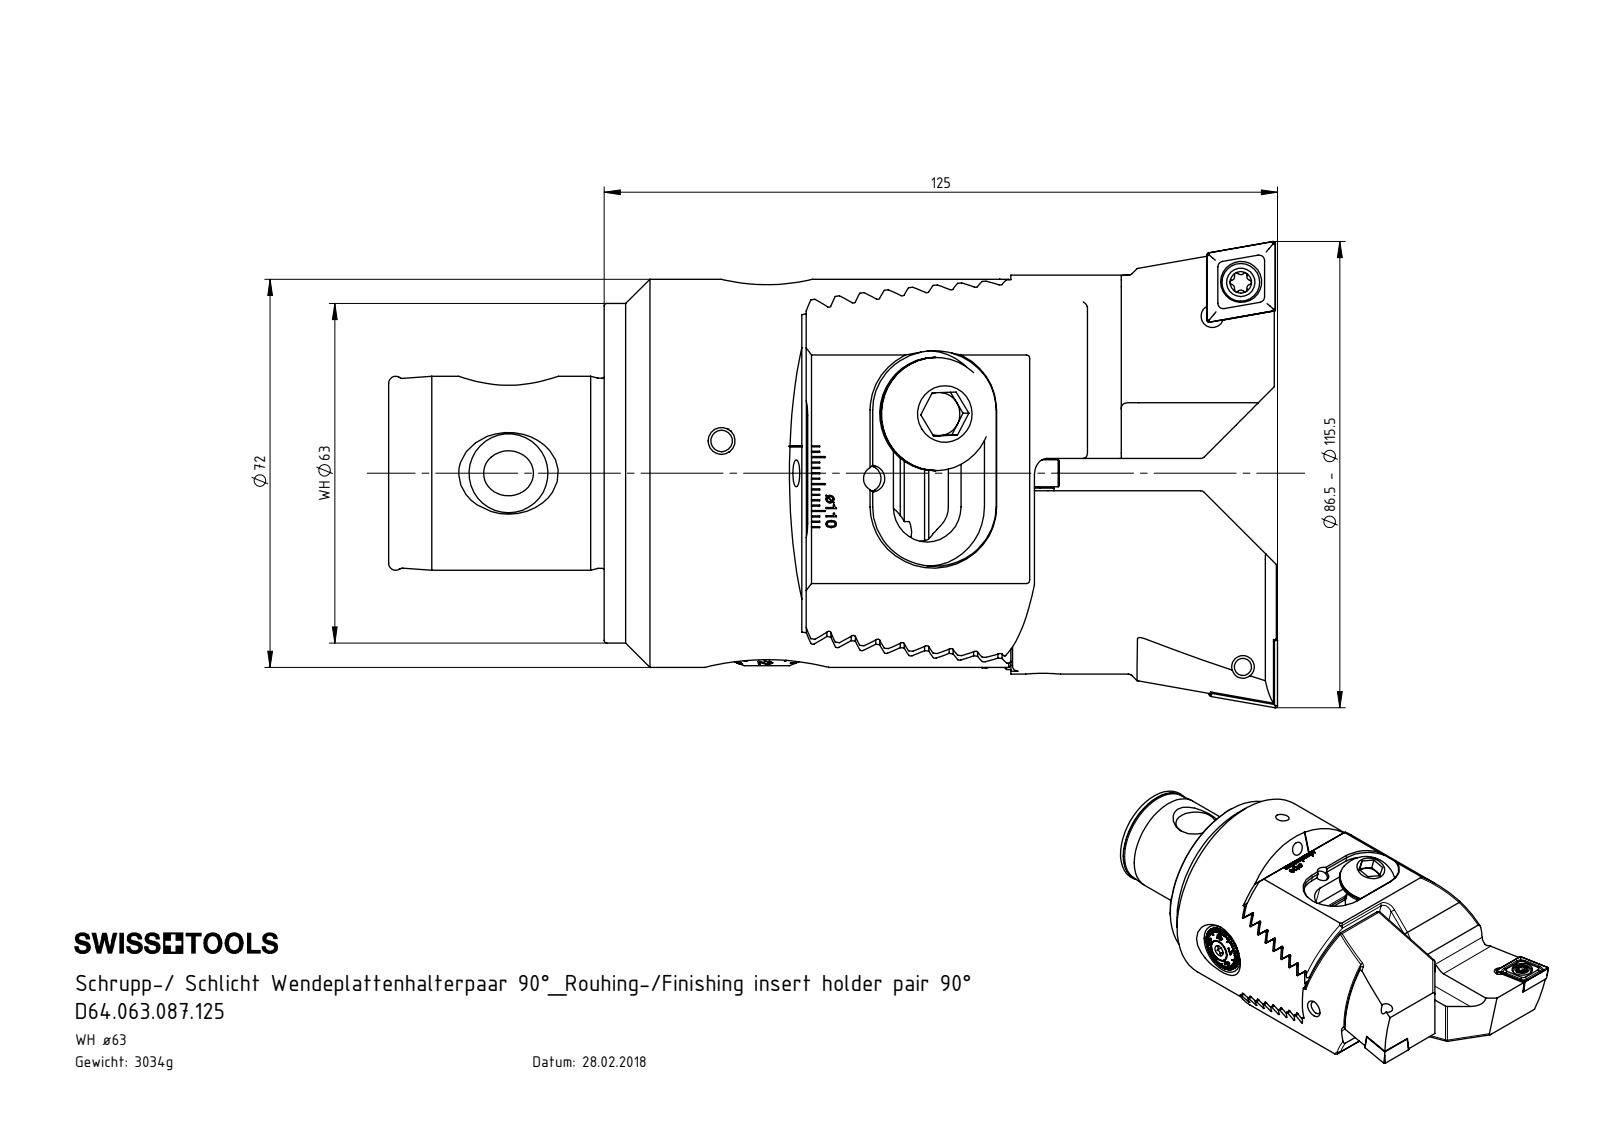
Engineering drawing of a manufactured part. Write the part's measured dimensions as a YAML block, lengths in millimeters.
part_name: "ZC7-WCC.010.050; ZC7-xxx.001.050_A_versetzt Combi; F32-BG2.017.003_A; D64.063.087.125 (+8 more)"
step_written_by: "SolidWorks 2017 (CONFIG_CONTROL_DESIGN)"
units: millimeters
bodies: {solids: 22, faces: 1551, planar: 797, cylindrical: 289, other: 465}
overall_size: [165, 86.5, 72]
volume: 387635
surface_area: 89754
round_holes:
  - {diameter: 5, count: 7}
  - {diameter: 4.2, count: 4}
  - {diameter: 2, count: 2}
  - {diameter: 3, count: 2}
  - {diameter: 5.5, count: 2}
  - {diameter: 7.6, count: 2}
  - {diameter: 10.25, count: 2}
  - {diameter: 13, count: 2}
  - {diameter: 13.5, count: 2}
  - {diameter: 2.5, count: 1}
  - {diameter: 2.9, count: 1}
  - {diameter: 3.3, count: 1}
round_bosses_or_shafts:
  - {diameter: 21, count: 4}
  - {diameter: 5, count: 4}
  - {diameter: 12, count: 2}
  - {diameter: 7, count: 2}
  - {diameter: 4, count: 2}
  - {diameter: 72, count: 1}
  - {diameter: 63, count: 1}
  - {diameter: 36, count: 1}
partial_cylinders:
  - {radius: 0.34, count: 18}
  - {radius: 0.34, count: 16}
  - {radius: 1, count: 16}
  - {radius: 0.39, count: 12}
  - {radius: 0.69, count: 8}
  - {radius: 0.69, count: 4}
  - {radius: 3, count: 4}
  - {radius: 6.5, count: 4}
face_to_face_distances: [4.07, 8.14, 12.21, 16.28, 4.01, 4.13, 20.35, 20.36, 24.43, 8.08]
hole_center_spacings: [8.21, 8.33, 71.43, 9, 9.84, 20, 51.3, 58.76]
